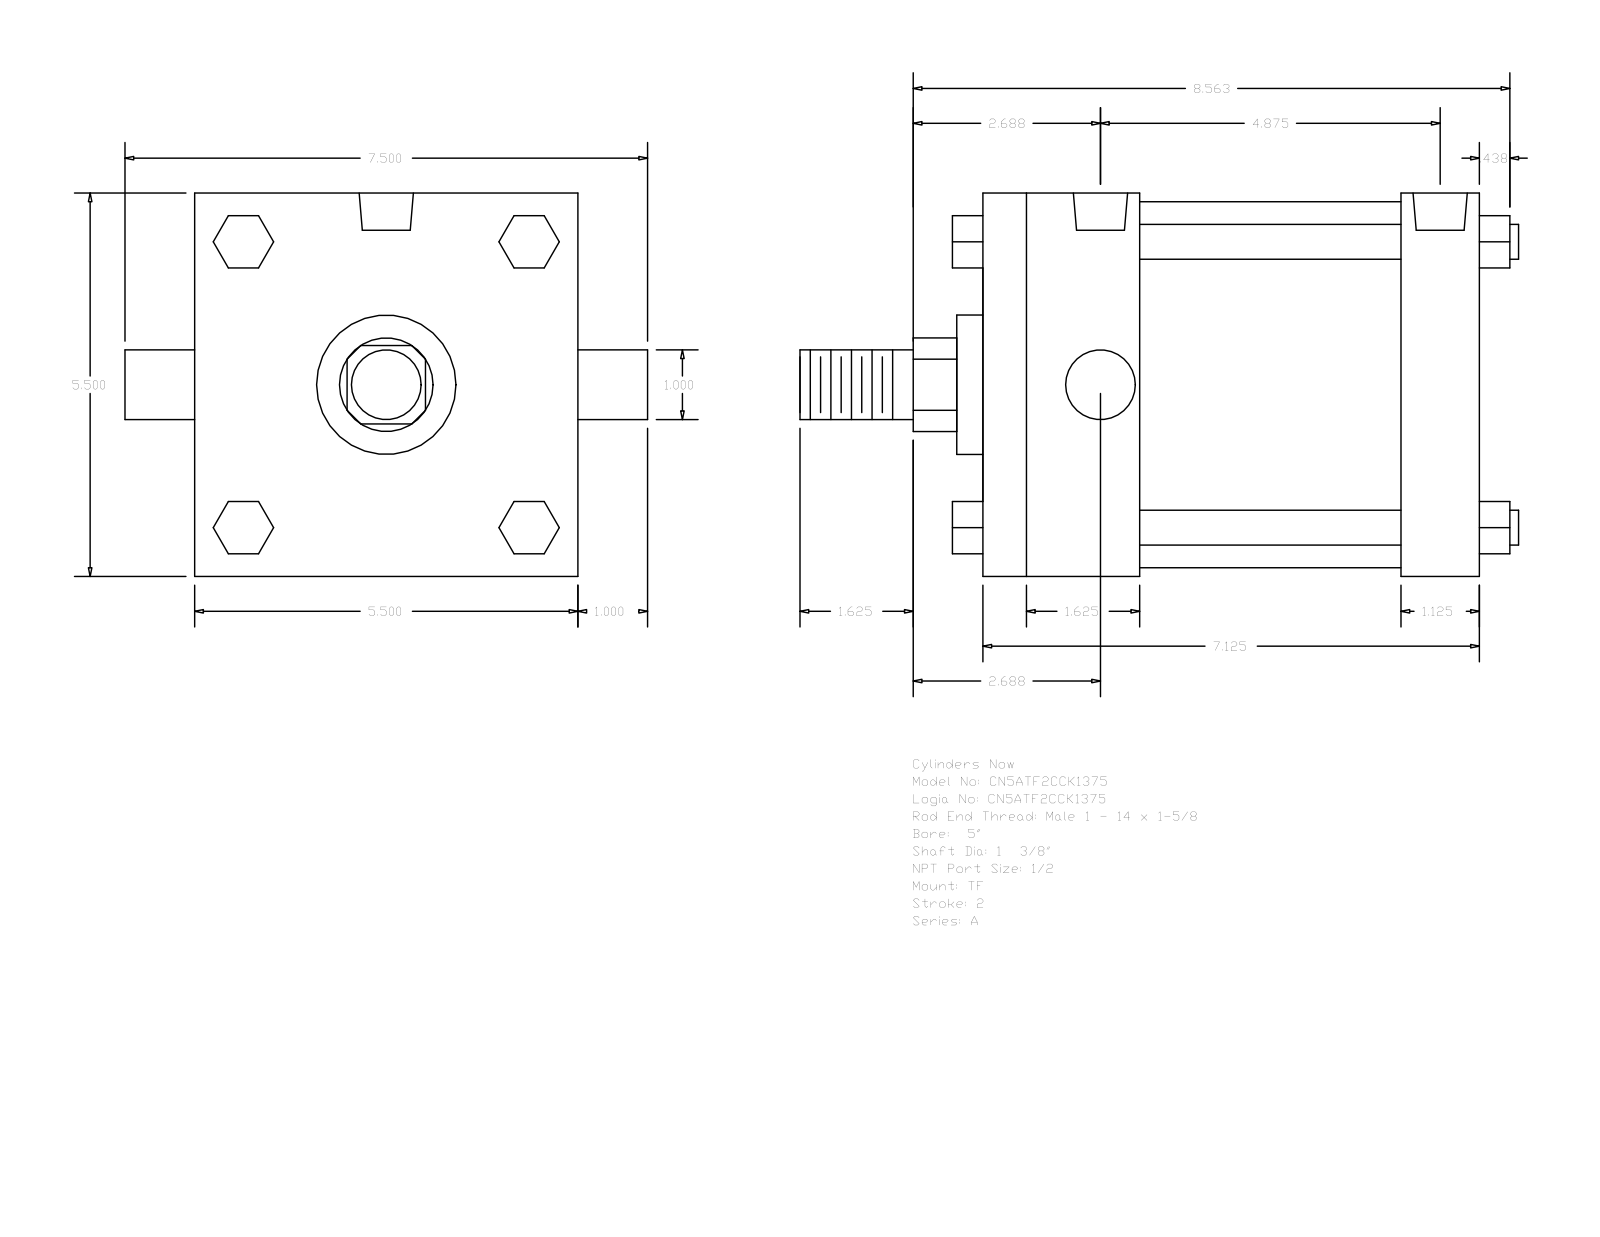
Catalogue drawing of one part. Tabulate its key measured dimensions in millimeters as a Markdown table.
| quantity | value |
| --- | --- |
| part name | A_TF__0500_1.375 |
| STEP written by | GSSL Pune (CONFIG_CONTROL_DESIGN) |
| units | millimeters |
| bodies | 0 solids, 120 faces (92 planar, 28 cylindrical, 0 other) |
| overall size | 261.94 × 190.5 × 139.7 |
| round holes (diameter × count) | 8.73 × 3, 19.77 × 2 |
| round bosses / shafts (diameter × count) | 12.7 × 4, 25.4 × 2, 133.35 × 1, 50.8 × 1, 34.92 × 1 |
| partial cylindrical surfaces (radius × count) | 17.06 × 1 |
| main face-to-face distances | 139.7, 180.98, 57.15, 28.58, 152.4, 95.25, 123.83, 19.05, 52.07, 90.18 |
| hole center spacings | 2.39, 121.44, 119.05, 123.83 |
